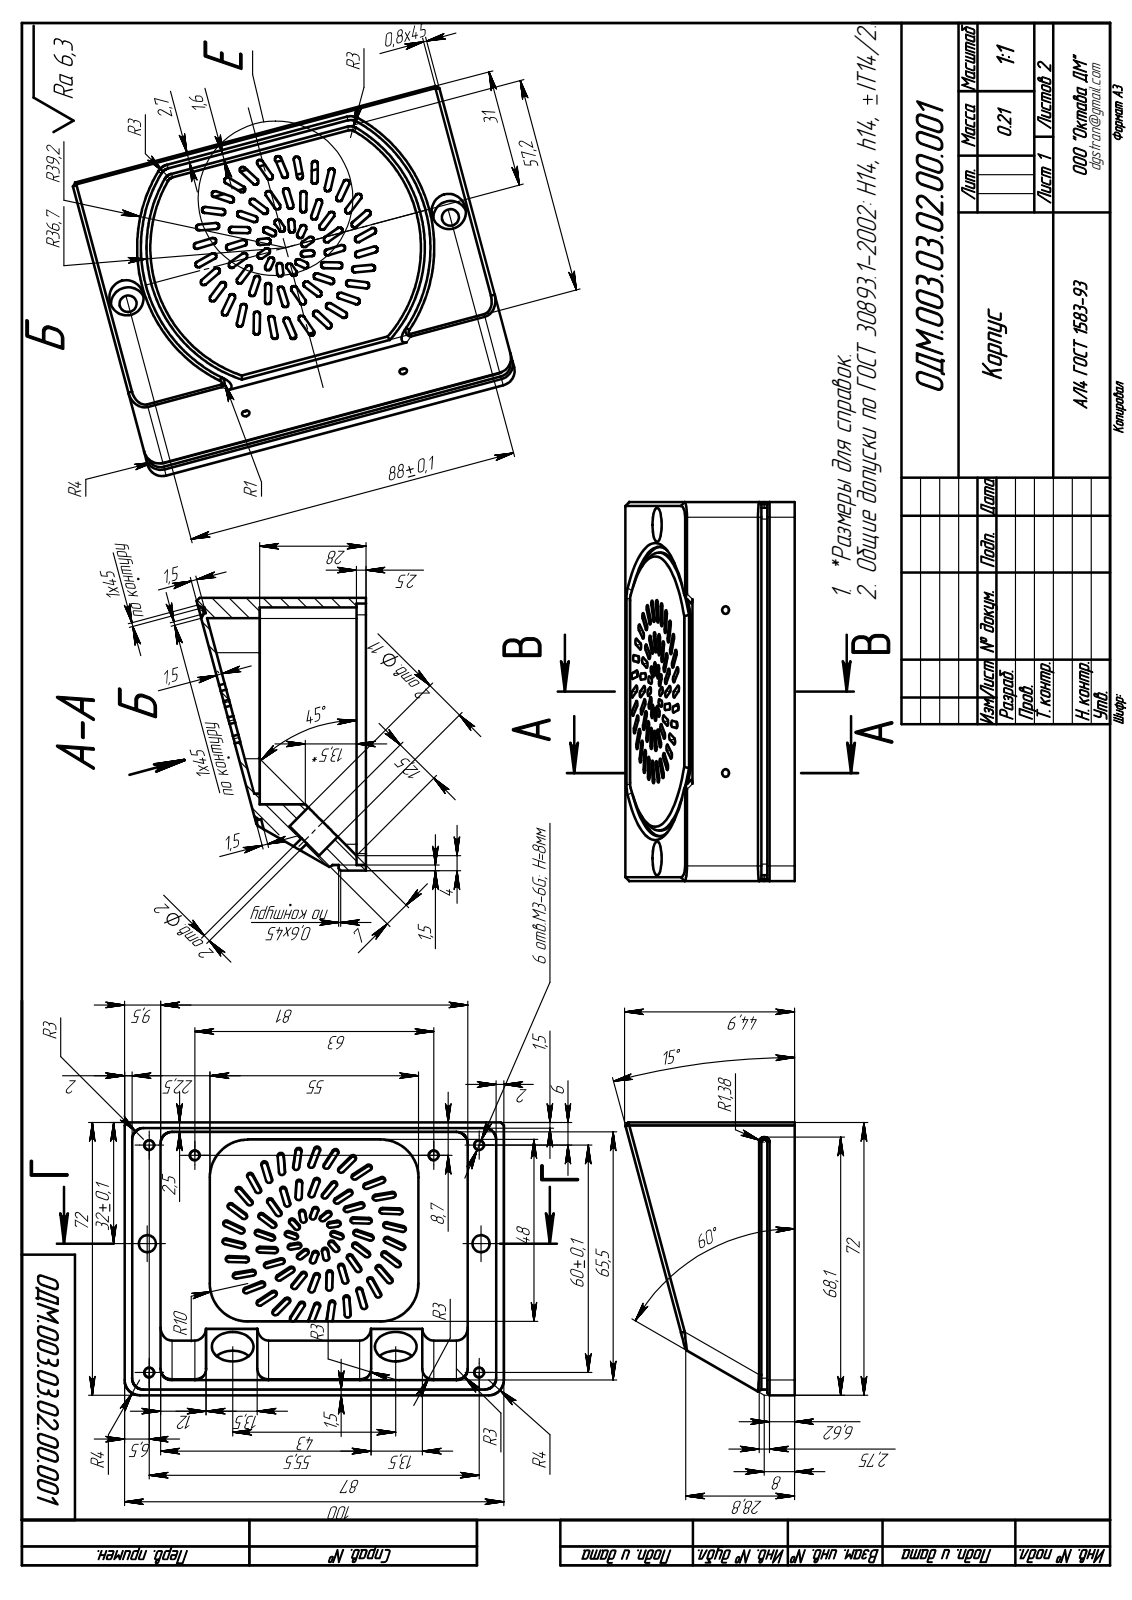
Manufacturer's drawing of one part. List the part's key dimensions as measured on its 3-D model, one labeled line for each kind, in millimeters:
Part name (STEP PRODUCT): ОДМ.003.03.02.00.001 Корпус
STEP written by: SolidWorks 2020 (AUTOMOTIVE_DESIGN)
Units: millimetres
Bodies: 1 solid, 491 faces (194 planar, 257 cylindrical, 40 other)
Overall size (bounding box): 100 × 72 × 44.65
Volume: 78 207 mm³ · Surface area: 37 888 mm²
Round holes (diameter × count): ⌀2.5 ×6, ⌀2 ×2, ⌀4.5 ×2, ⌀9 ×2, ⌀11 ×2
Partial cylindrical surfaces — rounded edges, fillets, slot ends (radius × count): R0.8 ×125, R3 ×25, R4 ×4, R10 ×4, R36.68 ×1, R38.18 ×1
Main face-to-face distances: 2.5, 1.5, 9.5, 90.5, 100, 25.5, 81, 68, 2, 69.5
Hole centre spacings: 43, 12.3, 26, 26.44, 34, 58.54, 60, 75.05
